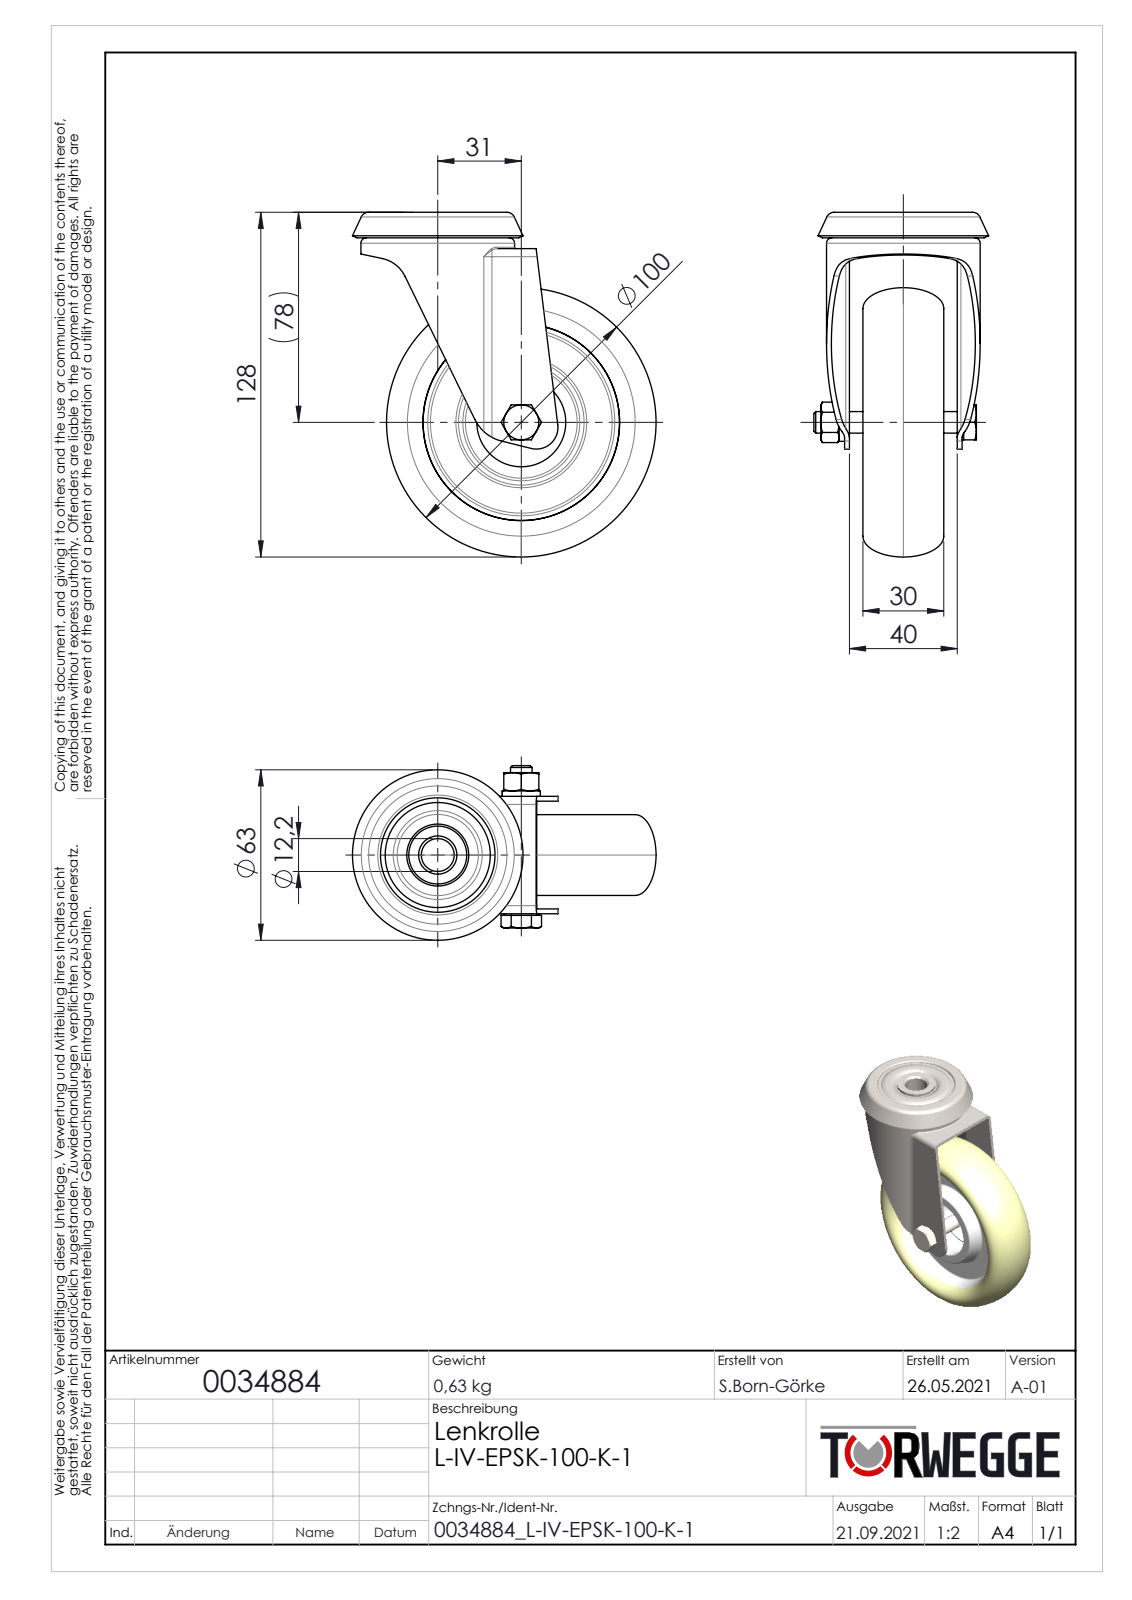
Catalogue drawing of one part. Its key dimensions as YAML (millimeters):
part_name: "0034884"
step_written_by: "SolidWorks 2020 (AUTOMOTIVE_DESIGN)"
units: millimeters
bodies: {solids: 22, faces: 316, planar: 70, cylindrical: 74, other: 172}
overall_size: [128, 112.64, 64.84]
volume: 198215
surface_area: 91129
round_holes:
  - {diameter: 6.8, count: 1}
  - {diameter: 8, count: 1}
  - {diameter: 8.1, count: 1}
  - {diameter: 8.3, count: 1}
  - {diameter: 12.2, count: 1}
  - {diameter: 20, count: 1}
  - {diameter: 31, count: 1}
  - {diameter: 33, count: 1}
  - {diameter: 35, count: 1}
  - {diameter: 53.4, count: 1}
round_bosses_or_shafts:
  - {diameter: 57, count: 1}
  - {diameter: 29, count: 1}
  - {diameter: 21.5, count: 1}
  - {diameter: 15, count: 1}
  - {diameter: 14.1, count: 1}
  - {diameter: 13, count: 1}
partial_cylinders:
  - {radius: 1.2, count: 2}
  - {radius: 3, count: 2}
  - {radius: 5, count: 2}
  - {radius: 6.8, count: 2}
  - {radius: 8, count: 1}
  - {radius: 12.01, count: 1}
  - {radius: 15, count: 1}
face_to_face_distances: [1.8, 18.8, 17, 23, 24.8, 41.8, 17.25, 5, 8.5, 16.3]
